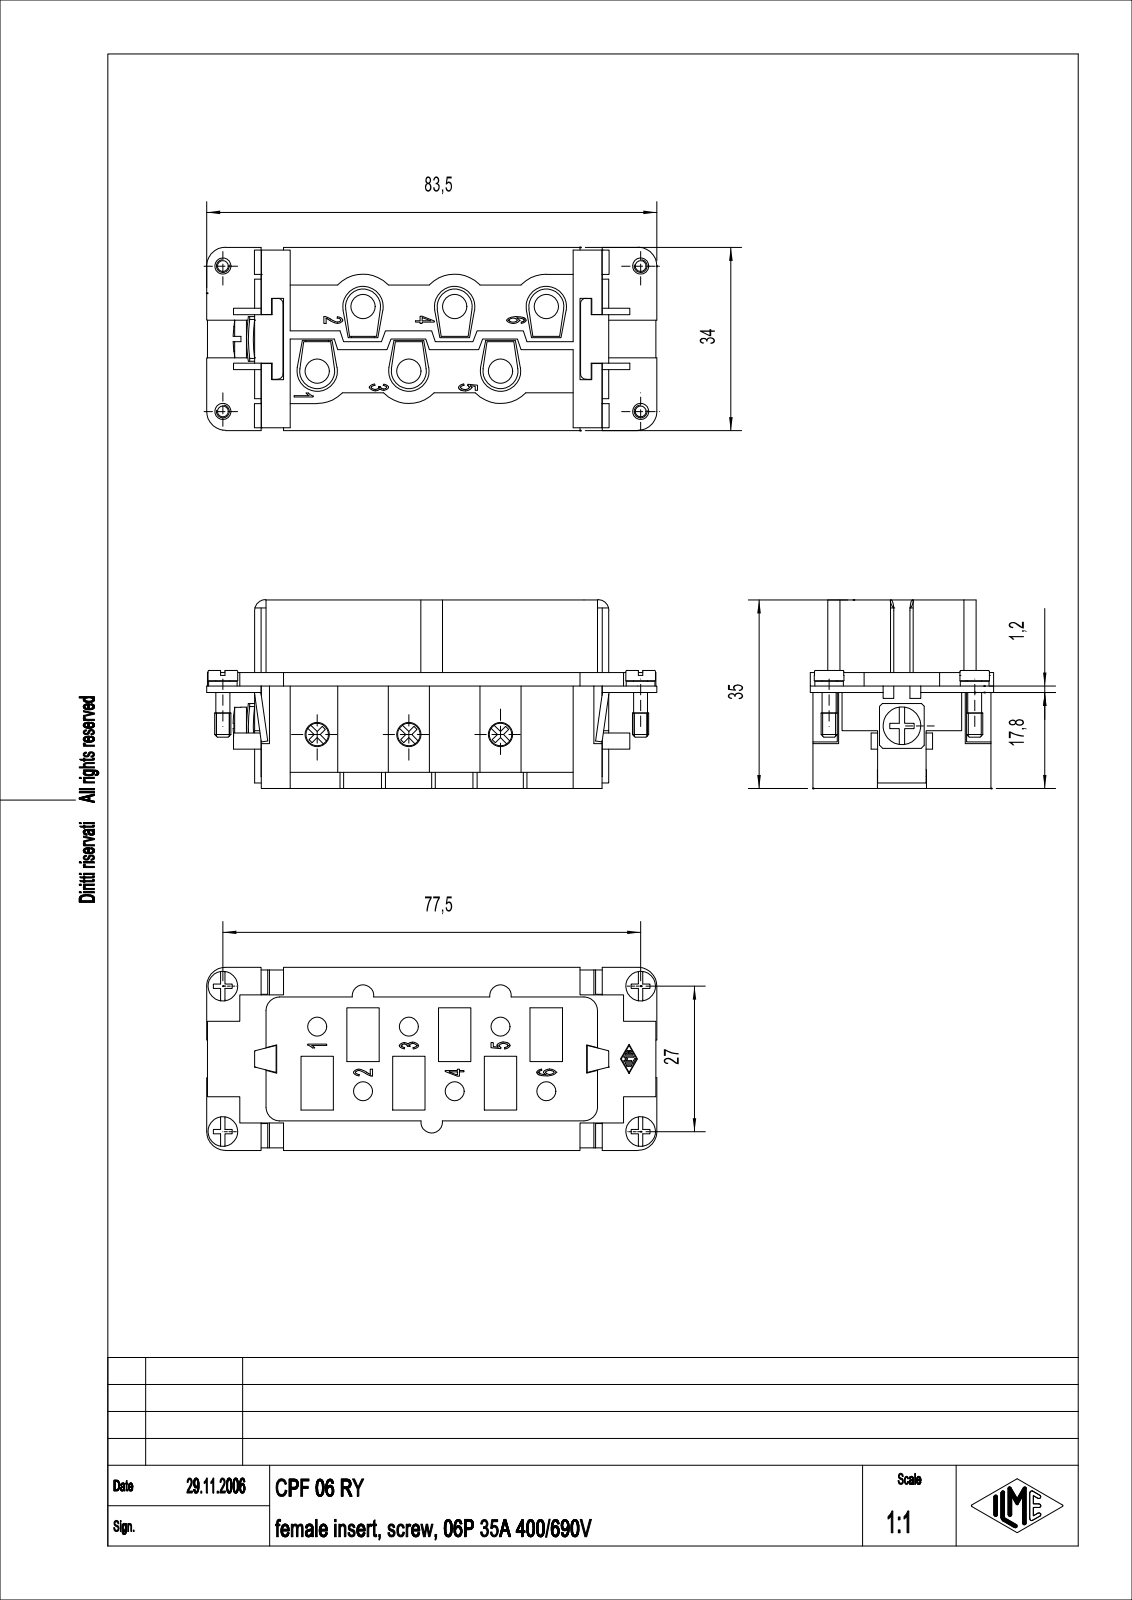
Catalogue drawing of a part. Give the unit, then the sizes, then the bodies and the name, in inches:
Units: inches
Overall size (bounding box): 3.287 × 1.378 × 1.339
Round holes (diameter × count): ⌀0.177 ×12, ⌀0.128 ×1
Round bosses / shafts (diameter × count): ⌀0.165 ×6, ⌀0.217 ×2, ⌀0.209 ×2, ⌀0.118 ×2, ⌀0.102 ×2, ⌀0.276 ×1
Partial cylindrical surfaces — rounded edges, fillets, slot ends (radius × count): R0.004 ×14, R0.128 ×6, R0.148 ×6, R0.256 ×6, R0.079 ×5, R0.098 ×4, R0.039 ×2, R0.138 ×2
Main face-to-face distances: 0.63, 0.098, 0.669, 0.335, 0.472, 0.906, 0.433, 0.02, 0.059, 0.531
Hole centre spacings: 0.669, 0.335, 0.579, 1.339, 1.004, 1.109, 1.673, 1.739
Volume: 2.673 in³ · Surface area: 39.26 in²
Bodies: 3 solids, 917 faces (497 planar, 130 cylindrical, 290 other)
Part name (STEP PRODUCT): CPF 06 RY
STEP written by: Autodesk Inventor 7 (AUTOMOTIVE_DESIGN)
